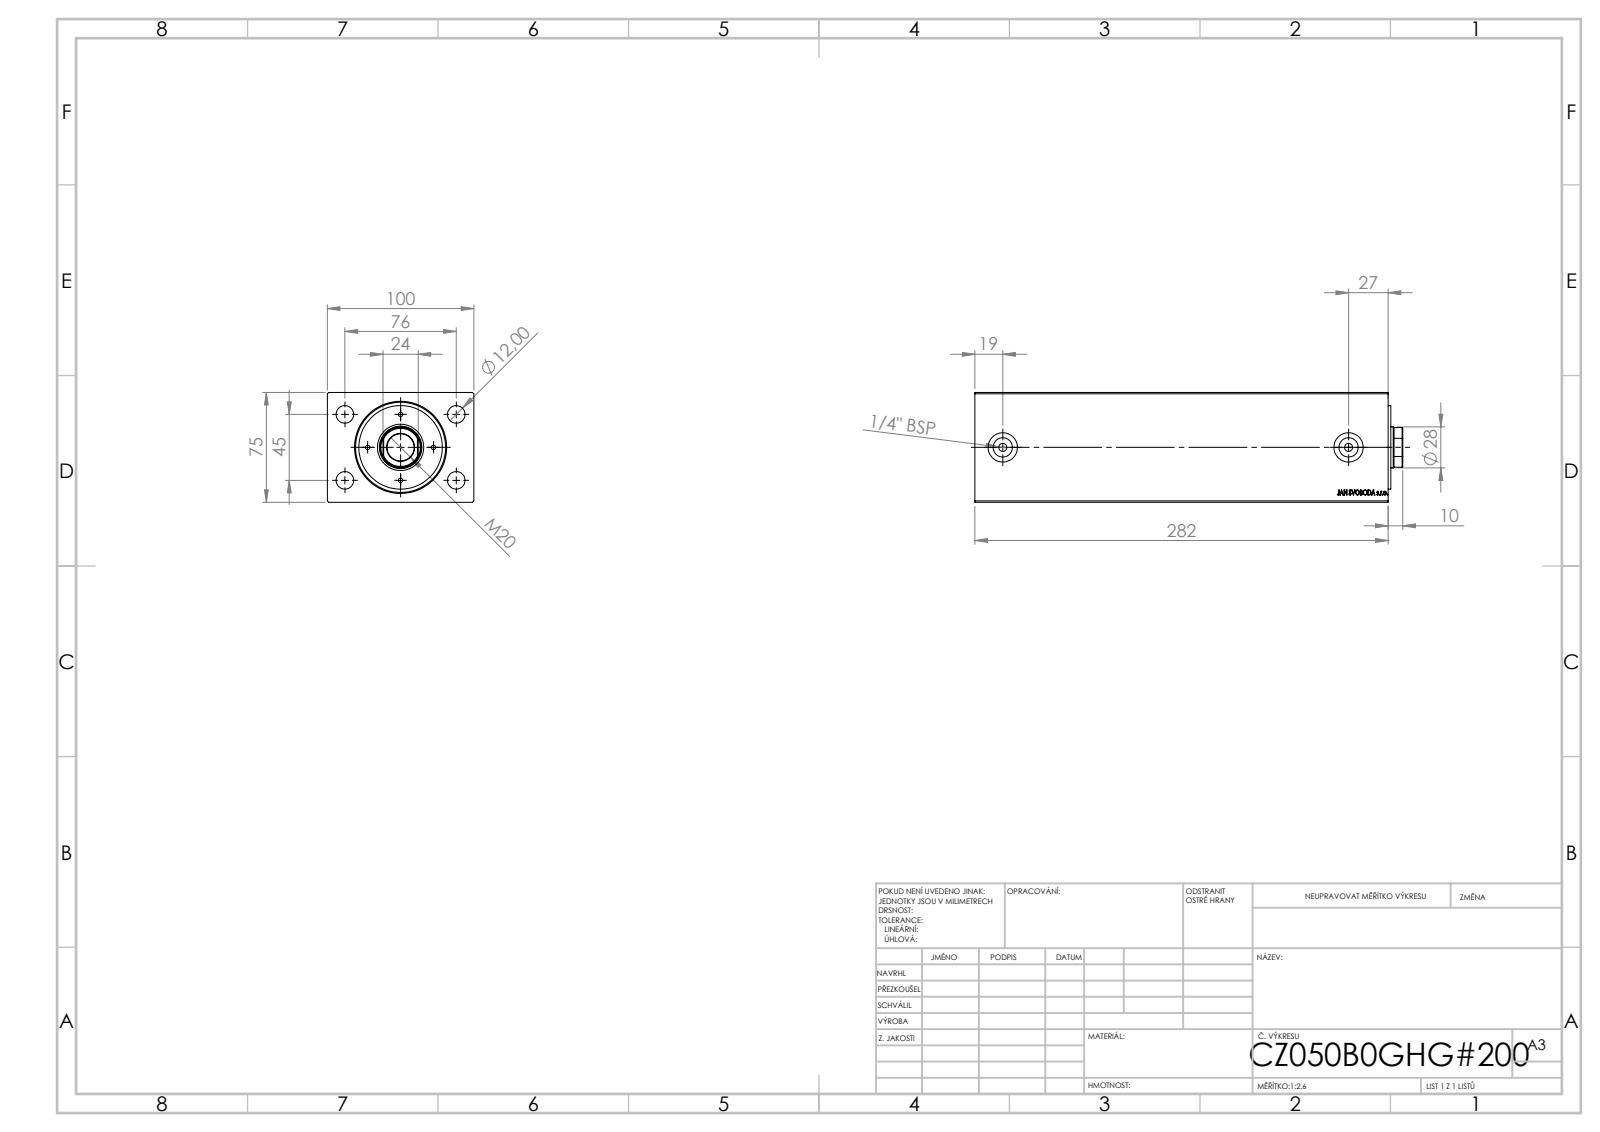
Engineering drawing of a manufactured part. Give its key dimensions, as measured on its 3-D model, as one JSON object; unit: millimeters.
{"part_name": "V500CZ; V500CZ_B_VC", "step_written_by": "SolidWorks 2019 (CONFIG_CONTROL_DESIGN)", "units": "millimeters", "bodies": {"solids": 3, "faces": 873, "planar": 399, "cylindrical": 58, "other": 416}, "overall_size": [292, 100, 75], "volume_mm3": 1887000, "surface_area_mm2": 226682, "round_holes": [[3, 4], [12, 4], [5.5, 2], [13.16, 2], [20, 2], [18.5, 1], [28, 1], [29, 1], [36, 1], [50, 1], [61.5, 1]], "round_bosses_or_shafts": [[57, 1]], "partial_cylinders_radius": [[13.5, 1]], "face_to_face_distances": [75, 100, 282, 264.5, 17.5, 82, 182.5, 200, 1.8, 83.8], "hole_center_spacings": [22.5, 27.32, 31.82, 38, 44.16, 45, 58.9, 64.55]}
